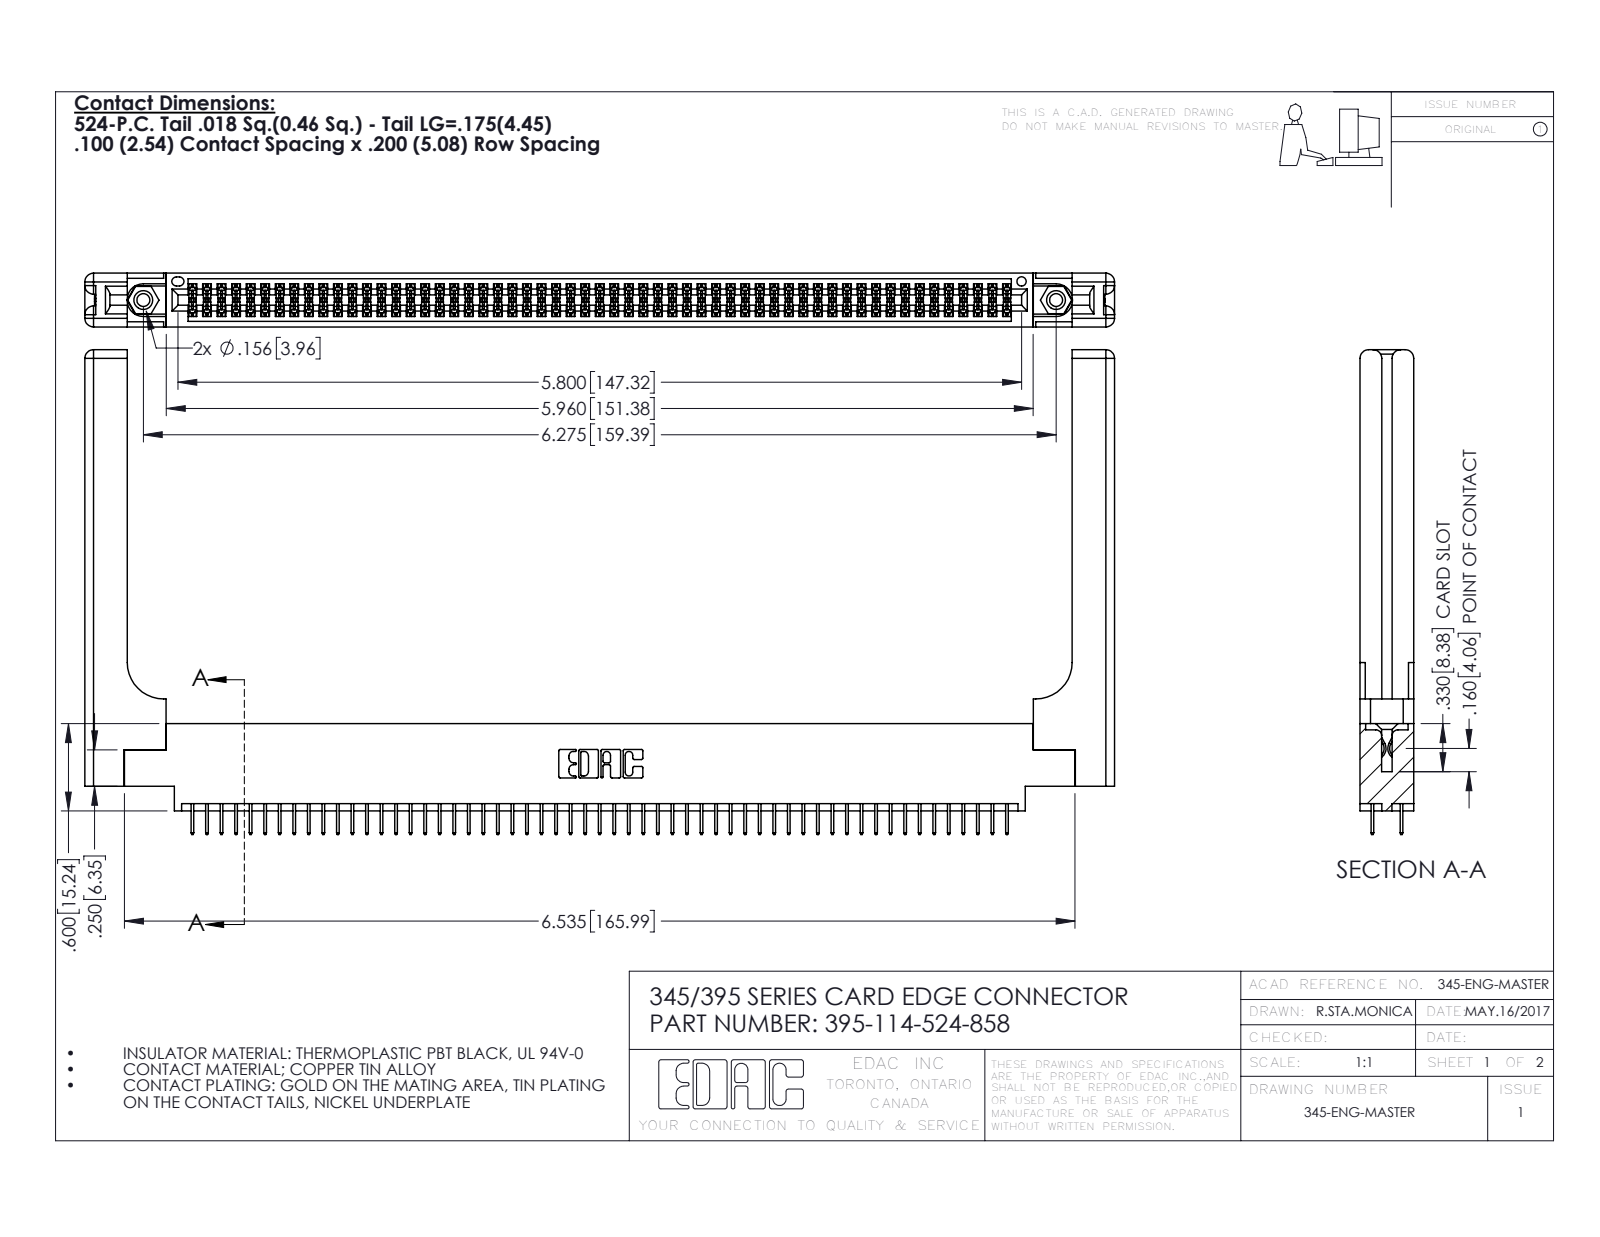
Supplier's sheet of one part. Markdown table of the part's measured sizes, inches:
| quantity | value |
| --- | --- |
| part name | 345-250-001_345-250-001-102; 395-114-524-858; 345 Part_0.170 Offset - 0.156 Dia-TH; 345-292-001_345-293-124 (+1 more) |
| STEP written by | SolidWorks 2016 (CONFIG_CONTROL_DESIGN) |
| units | inches |
| bodies | 119 solids, 6542 faces (4678 planar, 1804 cylindrical, 60 other) |
| overall size | 7.079 × 3.332 × 0.37 |
| volume | 1.574 in³ |
| surface area | 47.49 in² |
| round holes (diameter × count) | 0.089 × 2, 0.125 × 2, 0.156 × 2, 0.064 × 1 |
| round bosses / shafts (diameter × count) | 0.155 × 2 |
| partial cylindrical surfaces (radius × count) | 0.006 × 171, 0.01 × 22, 0.06 × 16, 0.007 × 6, 0.031 × 6, 0.026 × 3, 0.014 × 2, 0.019 × 2 |
| main face-to-face distances | 0.072, 0.37, 0.298, 0.2, 0.098, 0.272, 0.025, 0.225, 0.175, 0.148 |
| hole center spacings | 0.27, 6.039, 6.275 |
